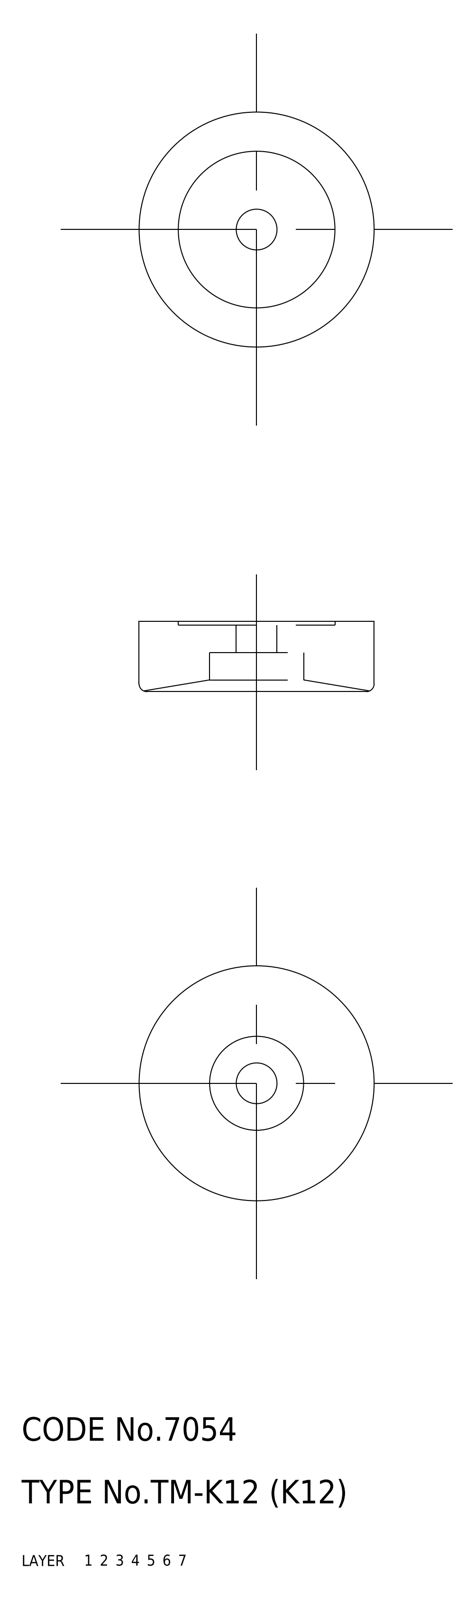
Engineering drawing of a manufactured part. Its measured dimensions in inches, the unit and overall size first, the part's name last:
Units: inches
Overall size (bounding box): 1.181 × 1.181 × 0.354
Volume: 0.319 in³ · Surface area: 3.734 in²
Bodies: 1 solid, 15 faces (0 planar, 0 cylindrical, 15 other)
Part name (STEP PRODUCT): rubber foot
STEP written by: CADfix (AUTOMOTIVE_DESIGN)
